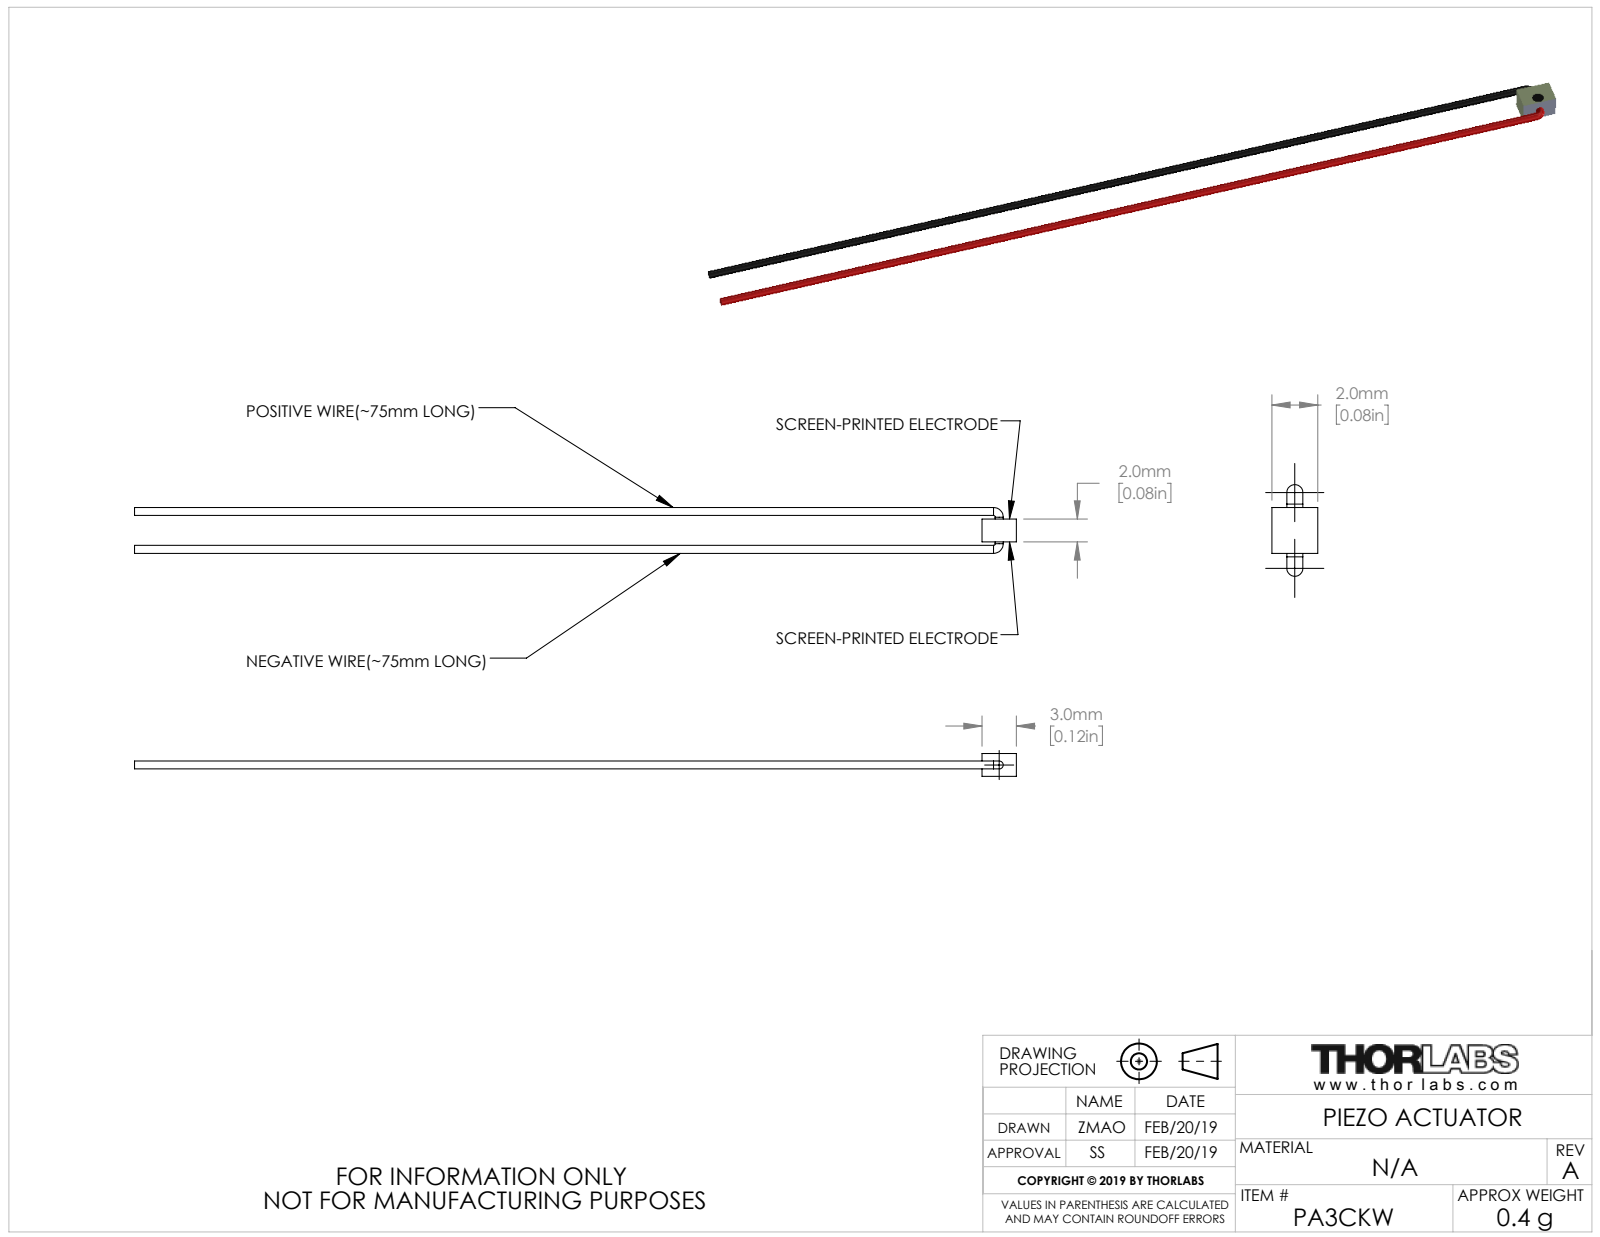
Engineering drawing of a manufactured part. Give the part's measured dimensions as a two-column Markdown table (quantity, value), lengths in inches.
| quantity | value |
| --- | --- |
| part name | CTN013621 |
| STEP written by | SolidWorks 2018 (AUTOMOTIVE_DESIGN) |
| units | inches |
| bodies | 1 solid, 23 faces (9 planar, 10 cylindrical, 4 other) |
| overall size | 3.031 × 0.158 × 0.079 |
| volume | 0.004 in³ |
| surface area | 0.567 in² |
| round holes (diameter × count) | 0.039 × 1 |
| round bosses / shafts (diameter × count) | 0.028 × 3 |
| main face-to-face distances | 0.079, 0.118, 0.078, 2.913, 3.031 |
